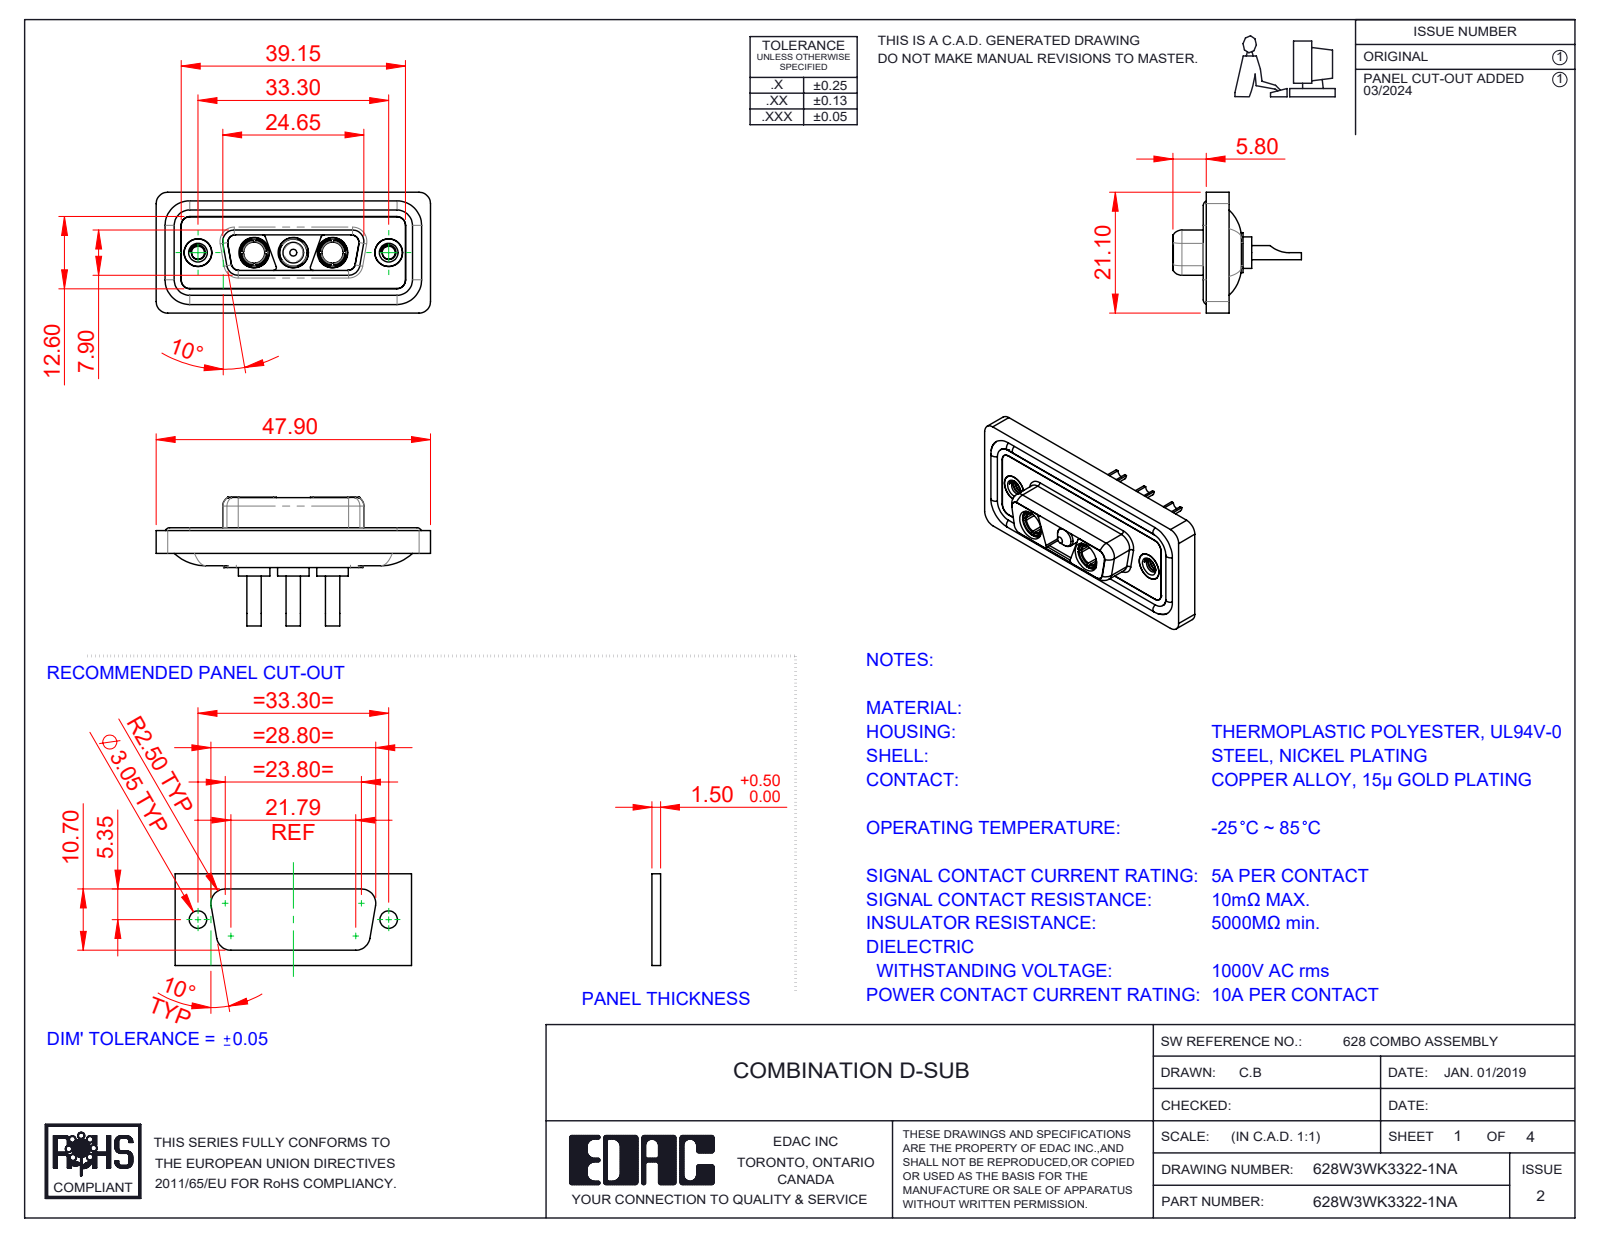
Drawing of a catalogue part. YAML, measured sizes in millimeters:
part_name: "Power Pin_10A SC; 628Combo Housing_3WK3; Power Socket_10A SC; 628Combo Waterproof Housing_15 Contacts (+4 more)"
step_written_by: "SolidWorks 2023 (CONFIG_CONTROL_DESIGN)"
units: millimeters
bodies: {solids: 13, faces: 597, planar: 184, cylindrical: 269, other: 144}
overall_size: [47.9, 22.45, 21.1]
volume: 5871
surface_area: 9645
round_holes:
  - {diameter: 4.85, count: 5}
  - {diameter: 1.7, count: 3}
  - {diameter: 5.3, count: 3}
  - {diameter: 2.26, count: 2}
  - {diameter: 3.7, count: 2}
  - {diameter: 4, count: 2}
  - {diameter: 4.05, count: 2}
  - {diameter: 5, count: 2}
round_bosses_or_shafts:
  - {diameter: 1.6, count: 4}
  - {diameter: 5.5, count: 3}
  - {diameter: 5.2, count: 3}
  - {diameter: 4.75, count: 3}
  - {diameter: 3.75, count: 3}
  - {diameter: 2.5, count: 3}
  - {diameter: 4.96, count: 2}
  - {diameter: 4.95, count: 2}
partial_cylinders:
  - {radius: 1.5, count: 22}
  - {radius: 2, count: 20}
  - {radius: 1.35, count: 12}
  - {radius: 0.5, count: 8}
  - {radius: 1.6, count: 8}
  - {radius: 0.25, count: 4}
  - {radius: 0.6, count: 4}
  - {radius: 0.65, count: 4}
face_to_face_distances: [0.4, 1.6, 1.8, 0.5, 1.1, 2.9, 5.65, 7.05, 1.5, 5.35]
hole_center_spacings: [6.85, 9.8, 16.65, 23.5, 13.7, 33.3]
